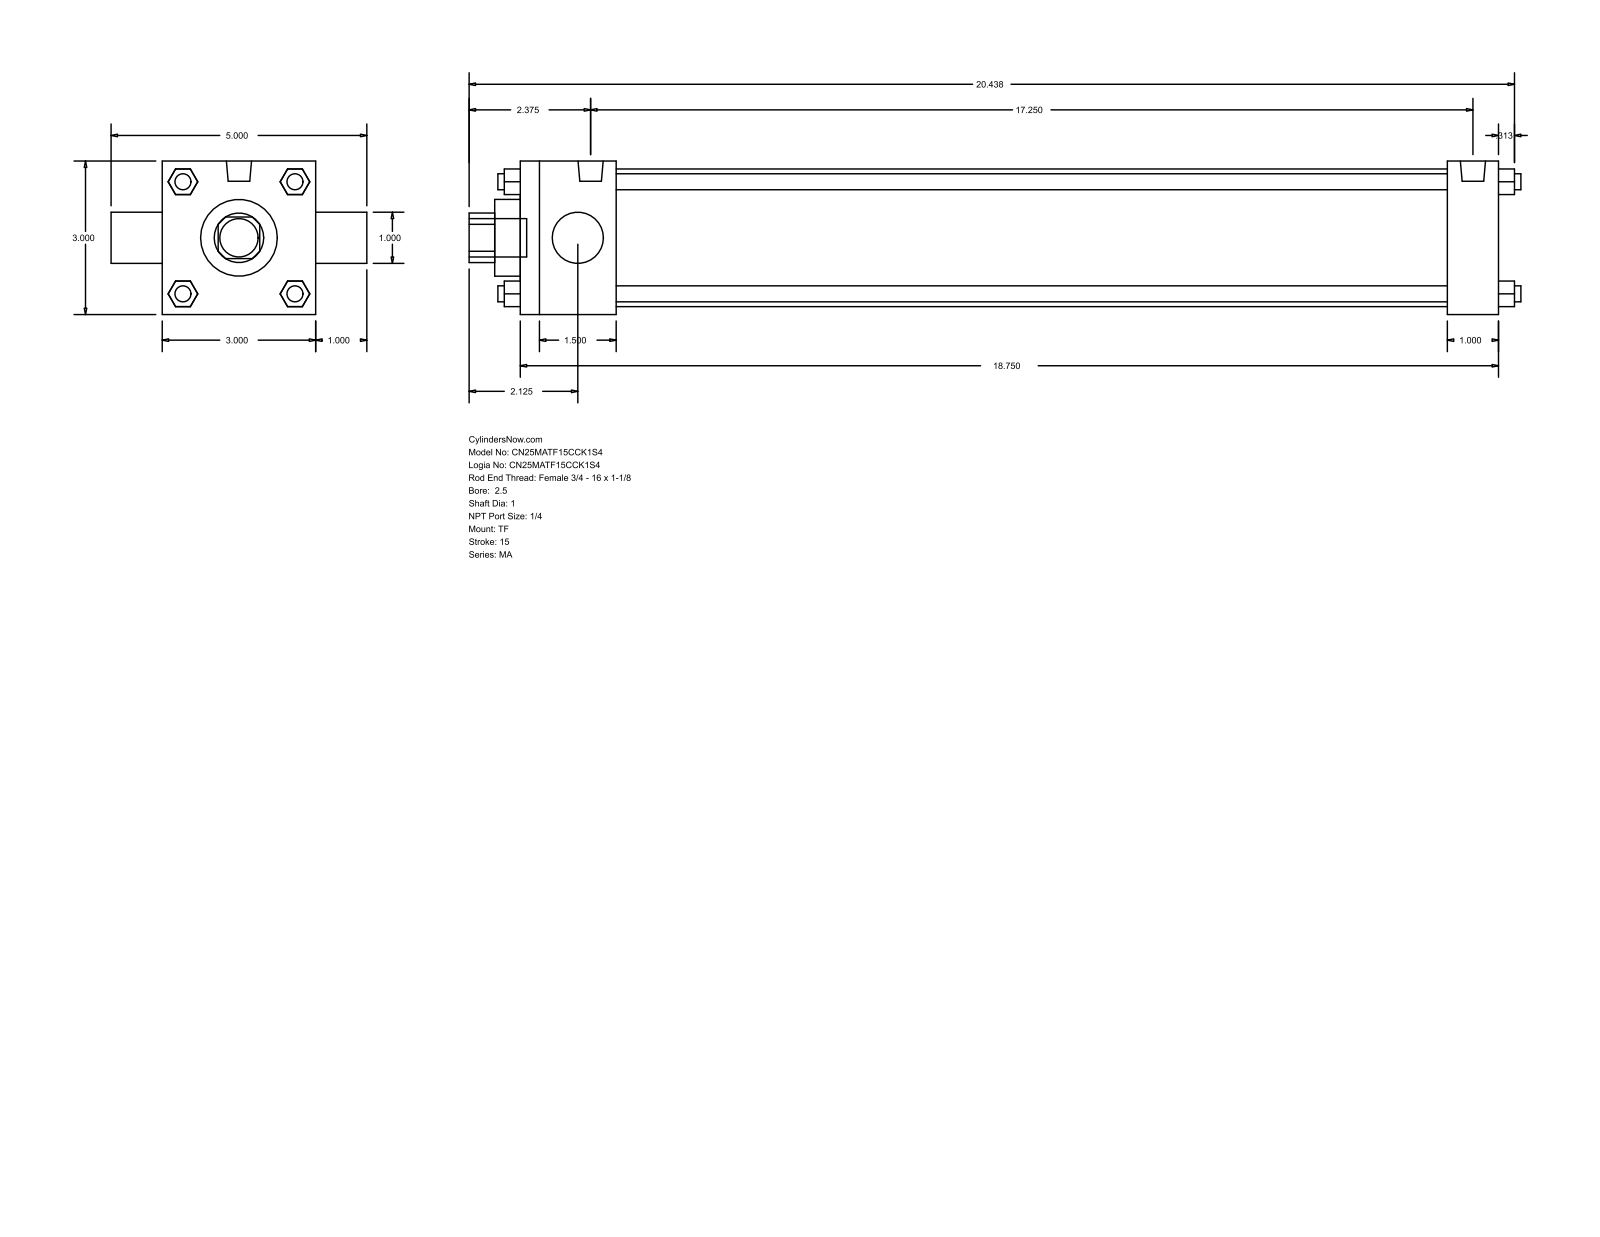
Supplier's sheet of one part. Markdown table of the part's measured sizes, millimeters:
| quantity | value |
| --- | --- |
| part name | MA_TF__0250_1 |
| STEP written by | GSSL Pune (CONFIG_CONTROL_DESIGN) |
| units | millimeters |
| bodies | 0 solids, 120 faces (92 planar, 28 cylindrical, 0 other) |
| overall size | 522.29 × 127 × 76.2 |
| round holes (diameter × count) | 25.4 × 2, 38.1 × 1, 68.33 × 1 |
| round bosses / shafts (diameter × count) | 7.94 × 7, 12.49 × 2, 19.05 × 1 |
| partial cylindrical surfaces (radius × count) | 12.29 × 1 |
| main face-to-face distances | 76.2, 485.78, 12.7, 47.63, 460.37, 412.74, 438.15, 25.41, 25.4, 101.6 |
